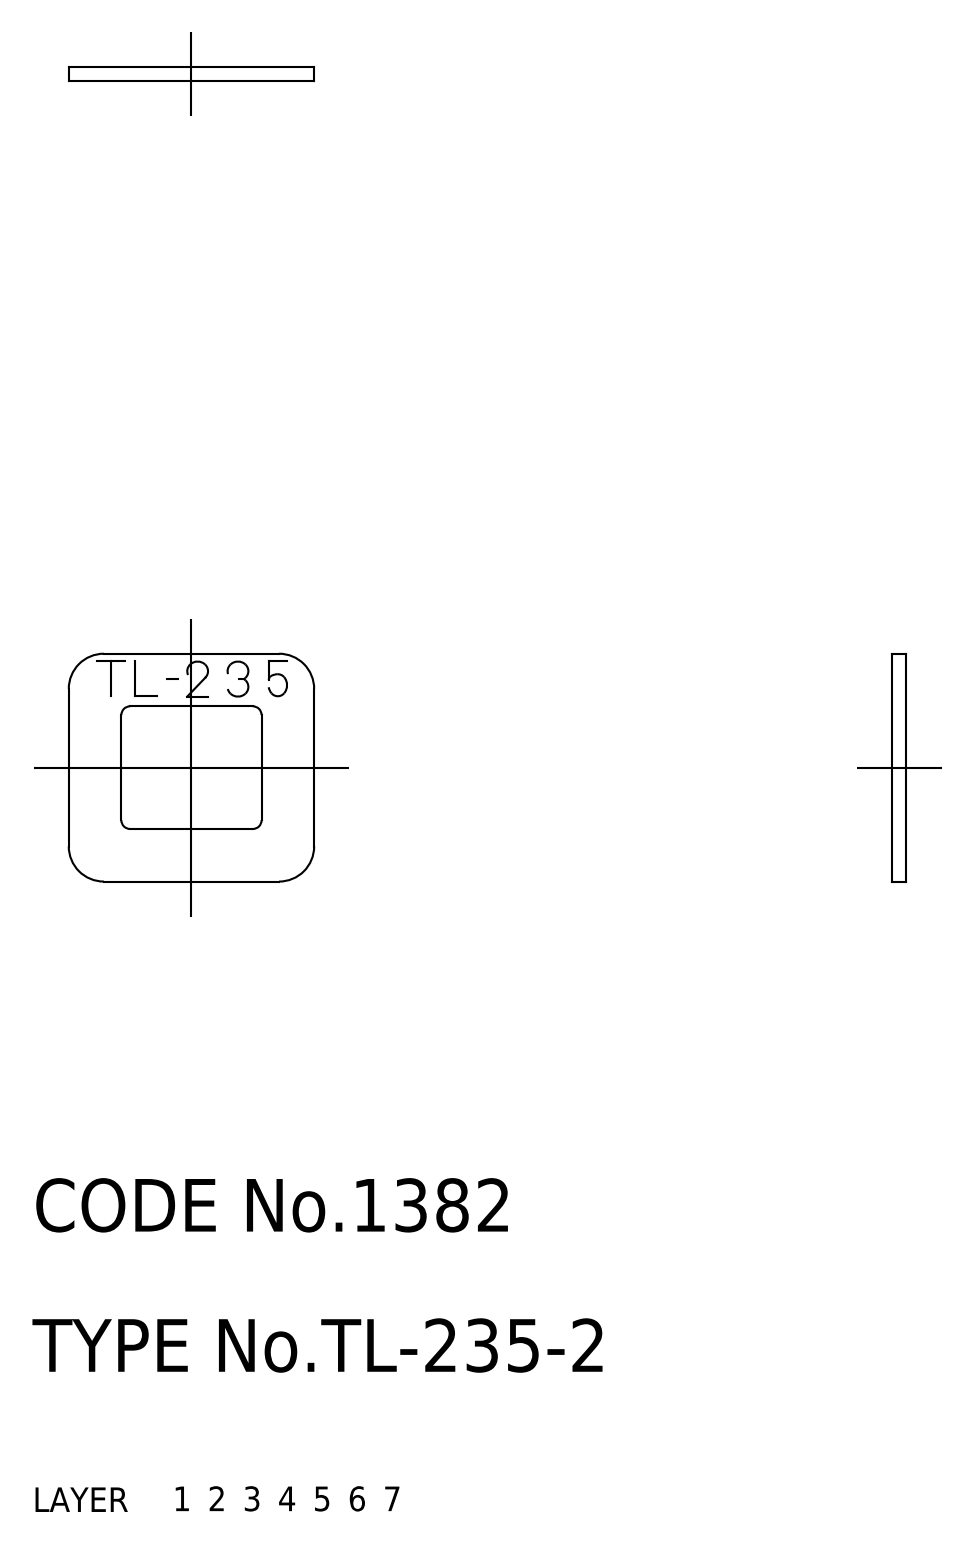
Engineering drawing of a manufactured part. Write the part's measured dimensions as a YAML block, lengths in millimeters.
part_name: "spacer"
step_written_by: "CADfix (AUTOMOTIVE_DESIGN)"
units: millimeters
bodies: {solids: 1, faces: 18, planar: 0, cylindrical: 0, other: 18}
overall_size: [14, 13, 0.8]
volume: 98
surface_area: 309
